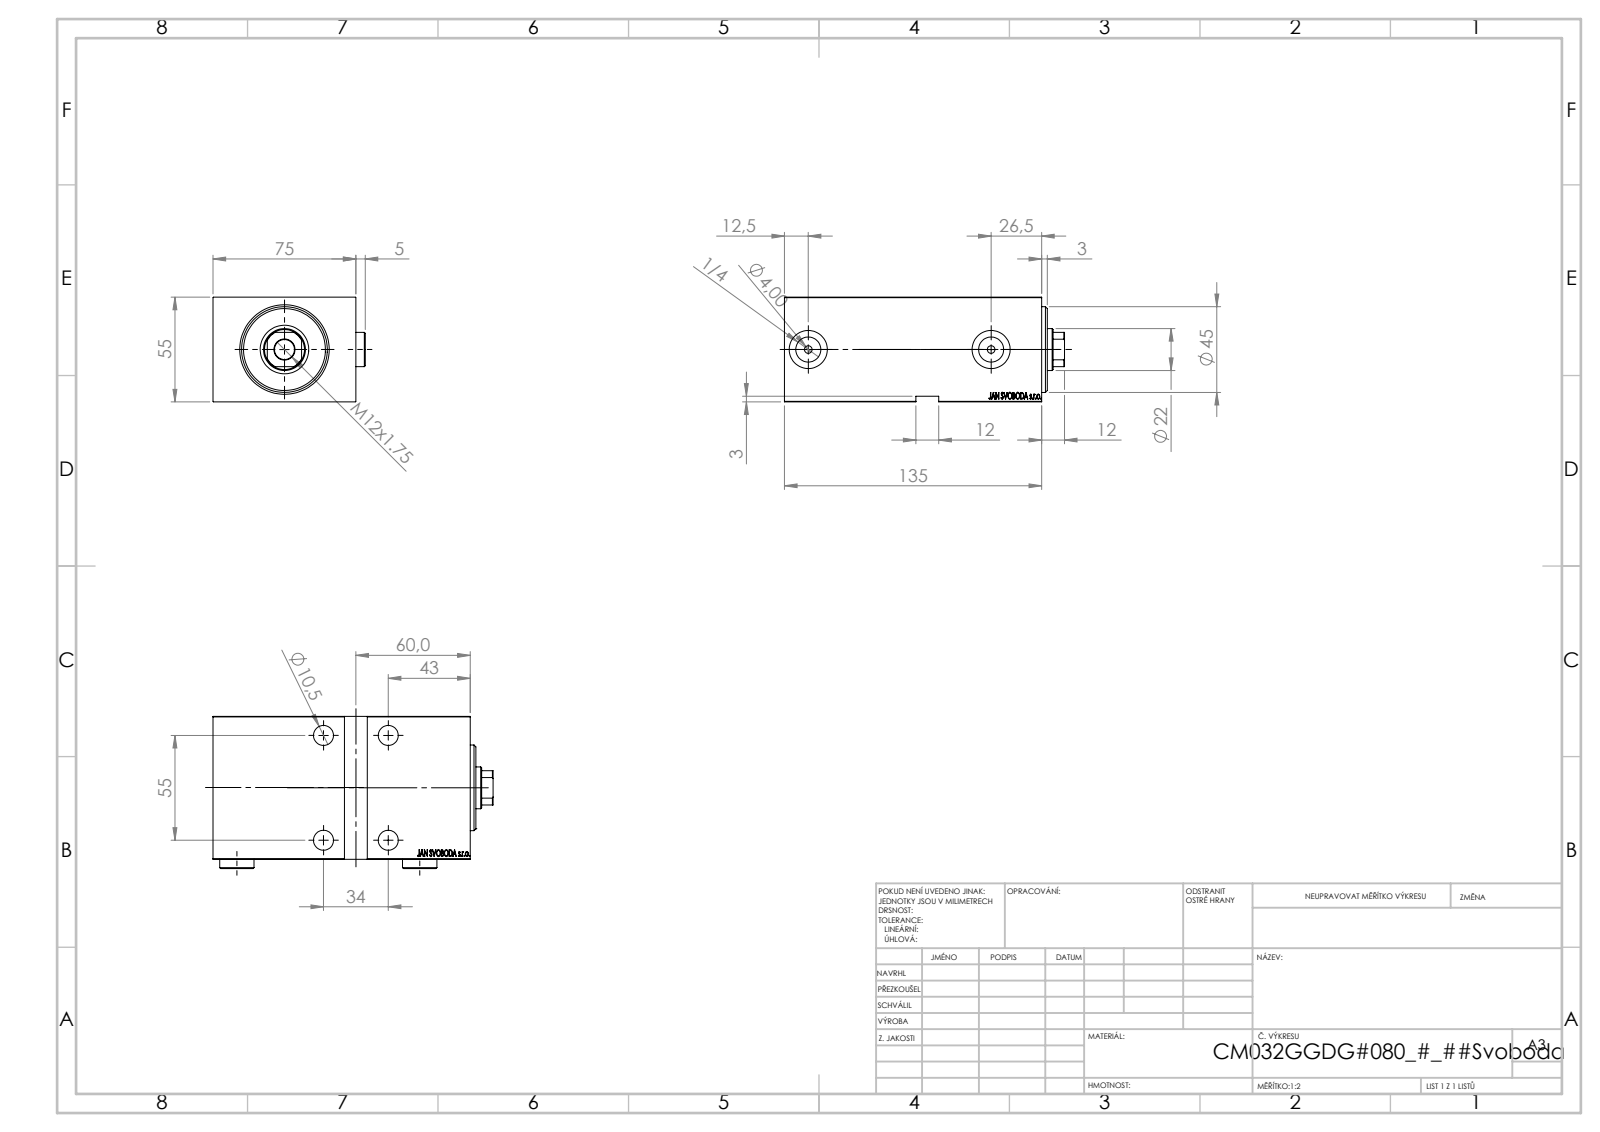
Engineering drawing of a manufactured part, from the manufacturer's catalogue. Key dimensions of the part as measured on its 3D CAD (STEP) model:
Part name (STEP PRODUCT): V450CM_VC_G; Zatka_OIL_PORT; V450CM_G_Body; V450CM_G_VCP
STEP written by: SolidWorks 2019 (CONFIG_CONTROL_DESIGN)
Units: millimetres
Bodies: 5 solids, 912 faces (446 planar, 68 cylindrical, 398 other)
Overall size (bounding box): 147 × 79.9 × 55
Volume: 491 329 mm³ · Surface area: 86 215 mm²
Round holes (diameter × count): ⌀10.5 ×5, ⌀16.5 ×4, ⌀4 ×2, ⌀13.16 ×2, ⌀20 ×2, ⌀22 ×1, ⌀25.5 ×1, ⌀32 ×1, ⌀34 ×1, ⌀45 ×1
Round bosses / shafts (diameter × count): ⌀18 ×2, ⌀27 ×1
Partial cylindrical surfaces — rounded edges, fillets, slot ends (radius × count): R10.5 ×1
Main face-to-face distances: 55, 75, 135, 5, 3, 130, 10, 120, 125, 74.9
Hole centre spacings: 34, 55, 64.66, 96
